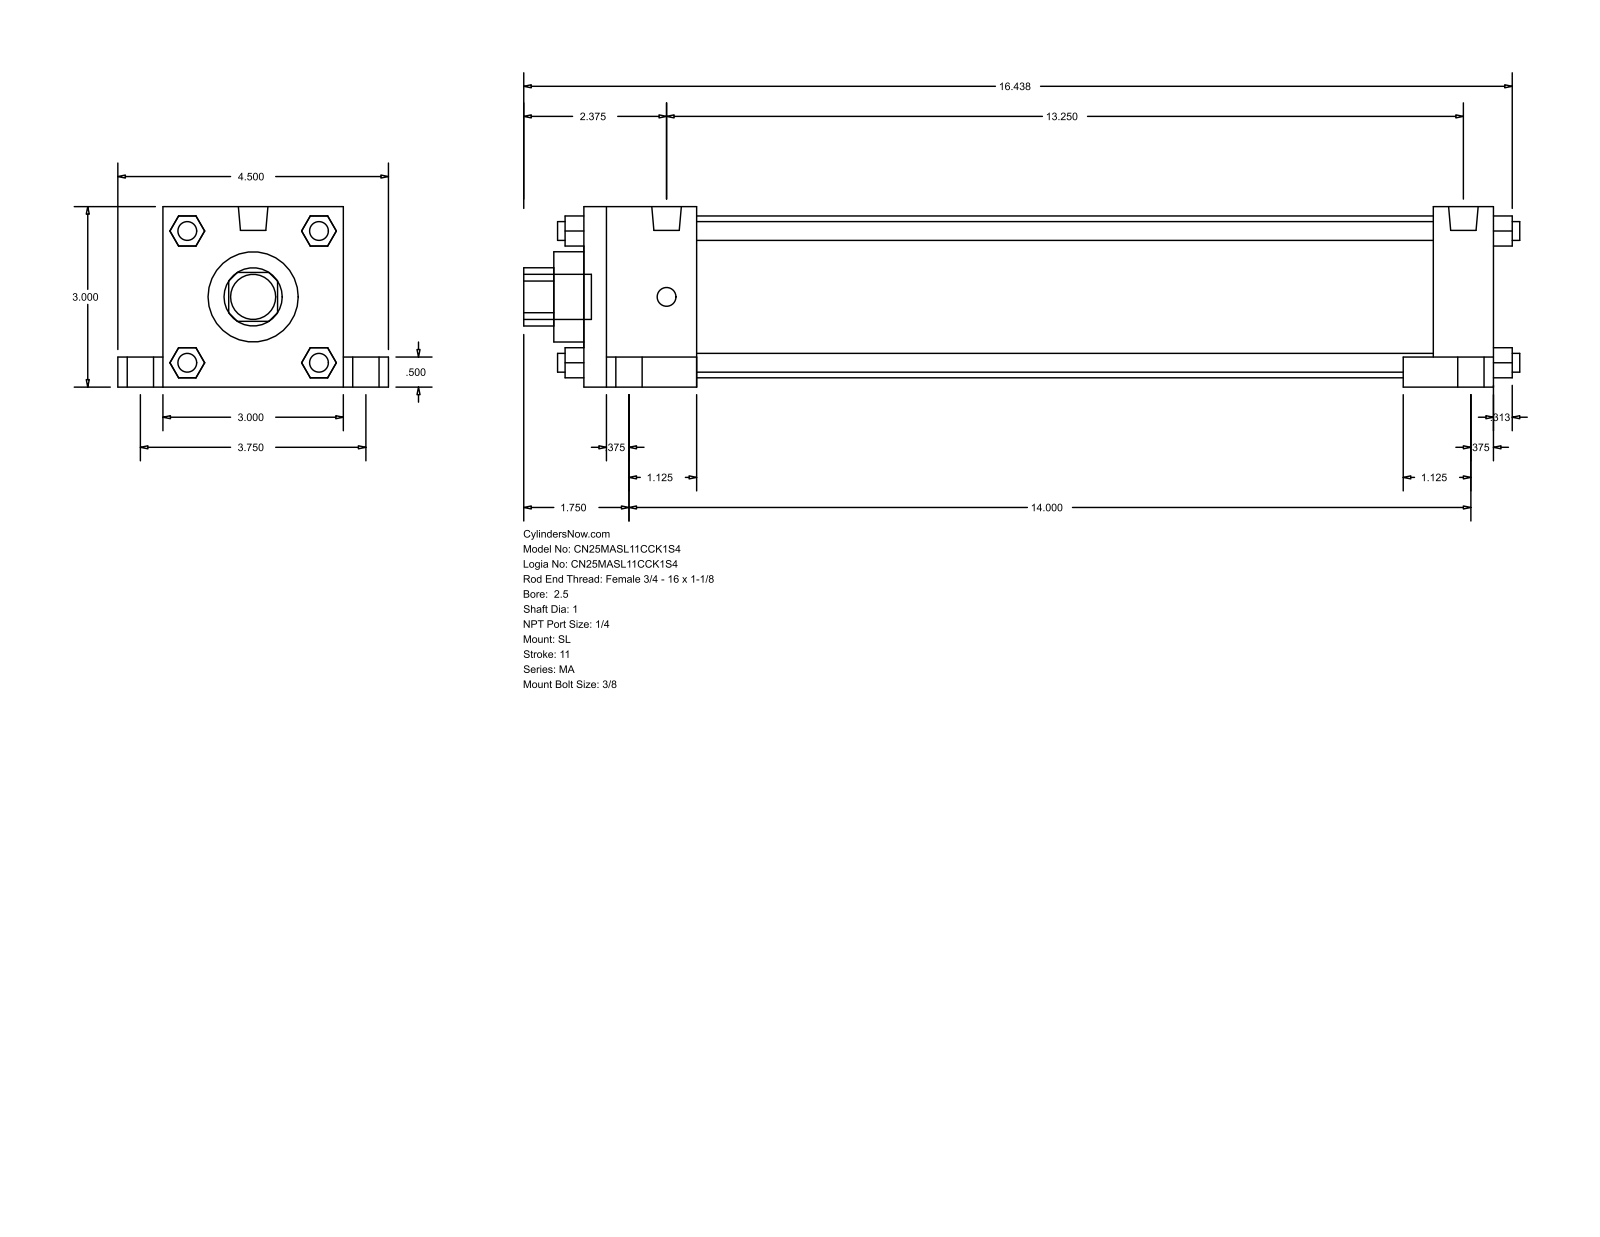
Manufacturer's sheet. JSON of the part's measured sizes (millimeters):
{"part_name": "MA_SL__0250_1", "step_written_by": "GSSL Pune (CONFIG_CONTROL_DESIGN)", "units": "millimeters", "bodies": {"solids": 0, "faces": 148, "planar": 112, "cylindrical": 36, "other": 0}, "overall_size": [420.69, 114.3, 76.2], "round_holes": [[25.4, 1], [38.1, 1], [68.33, 1]], "round_bosses_or_shafts": [[7.94, 8], [17.46, 4], [11.11, 4], [12.49, 2], [19.05, 1]], "partial_cylinders_radius": [[12.29, 1]], "face_to_face_distances": [76.2, 384.17, 12.7, 311.15, 25.39, 47.63, 336.54, 358.78, 19.05, 95.25]}
